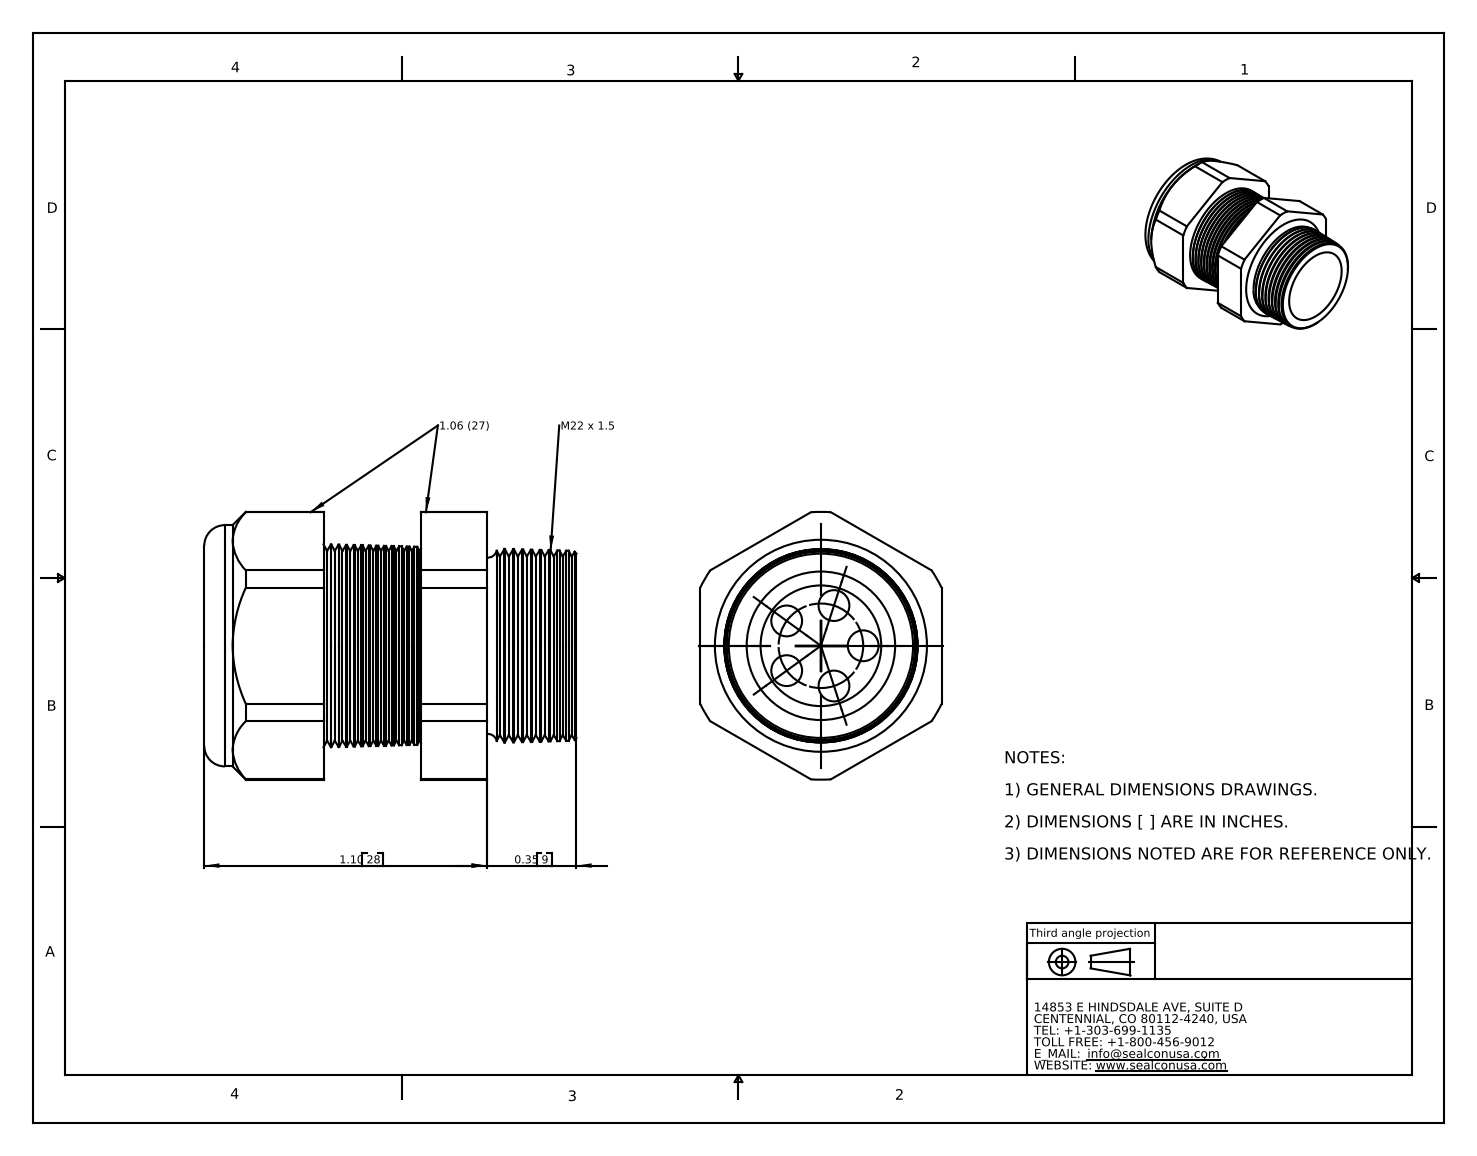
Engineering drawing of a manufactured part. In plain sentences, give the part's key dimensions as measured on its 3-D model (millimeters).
The part is named "CD22M4-GY". Its 3-D file was written by "SolidWorks 2007 (CONFIG_CONTROL_DESIGN)". It is 2 solids with 196 faces: 20 planar, 30 cylindrical and 146 other. Overall it measures 36.8 by 26.5 by 23.9 millimeters. Its volume is 9 540 cubic millimeters and its surface area 6 671 square millimeters. Round holes: 5 of diameter 3, 1 of diameter 11.4, 1 of diameter 11.9. Round bosses or shafts: 1 of diameter 23.9. Partial cylindrical surfaces (rounded edges, fillets, slot ends): 1 of radius 13.3. The main face-to-face distances are 23.9, 21.4, 11.8, 9.7, 27.9, 16.1, 6.5, 36.8, 25, 15.4. The hole center spacings are 4.9, 8, 4.2, 4.2.
